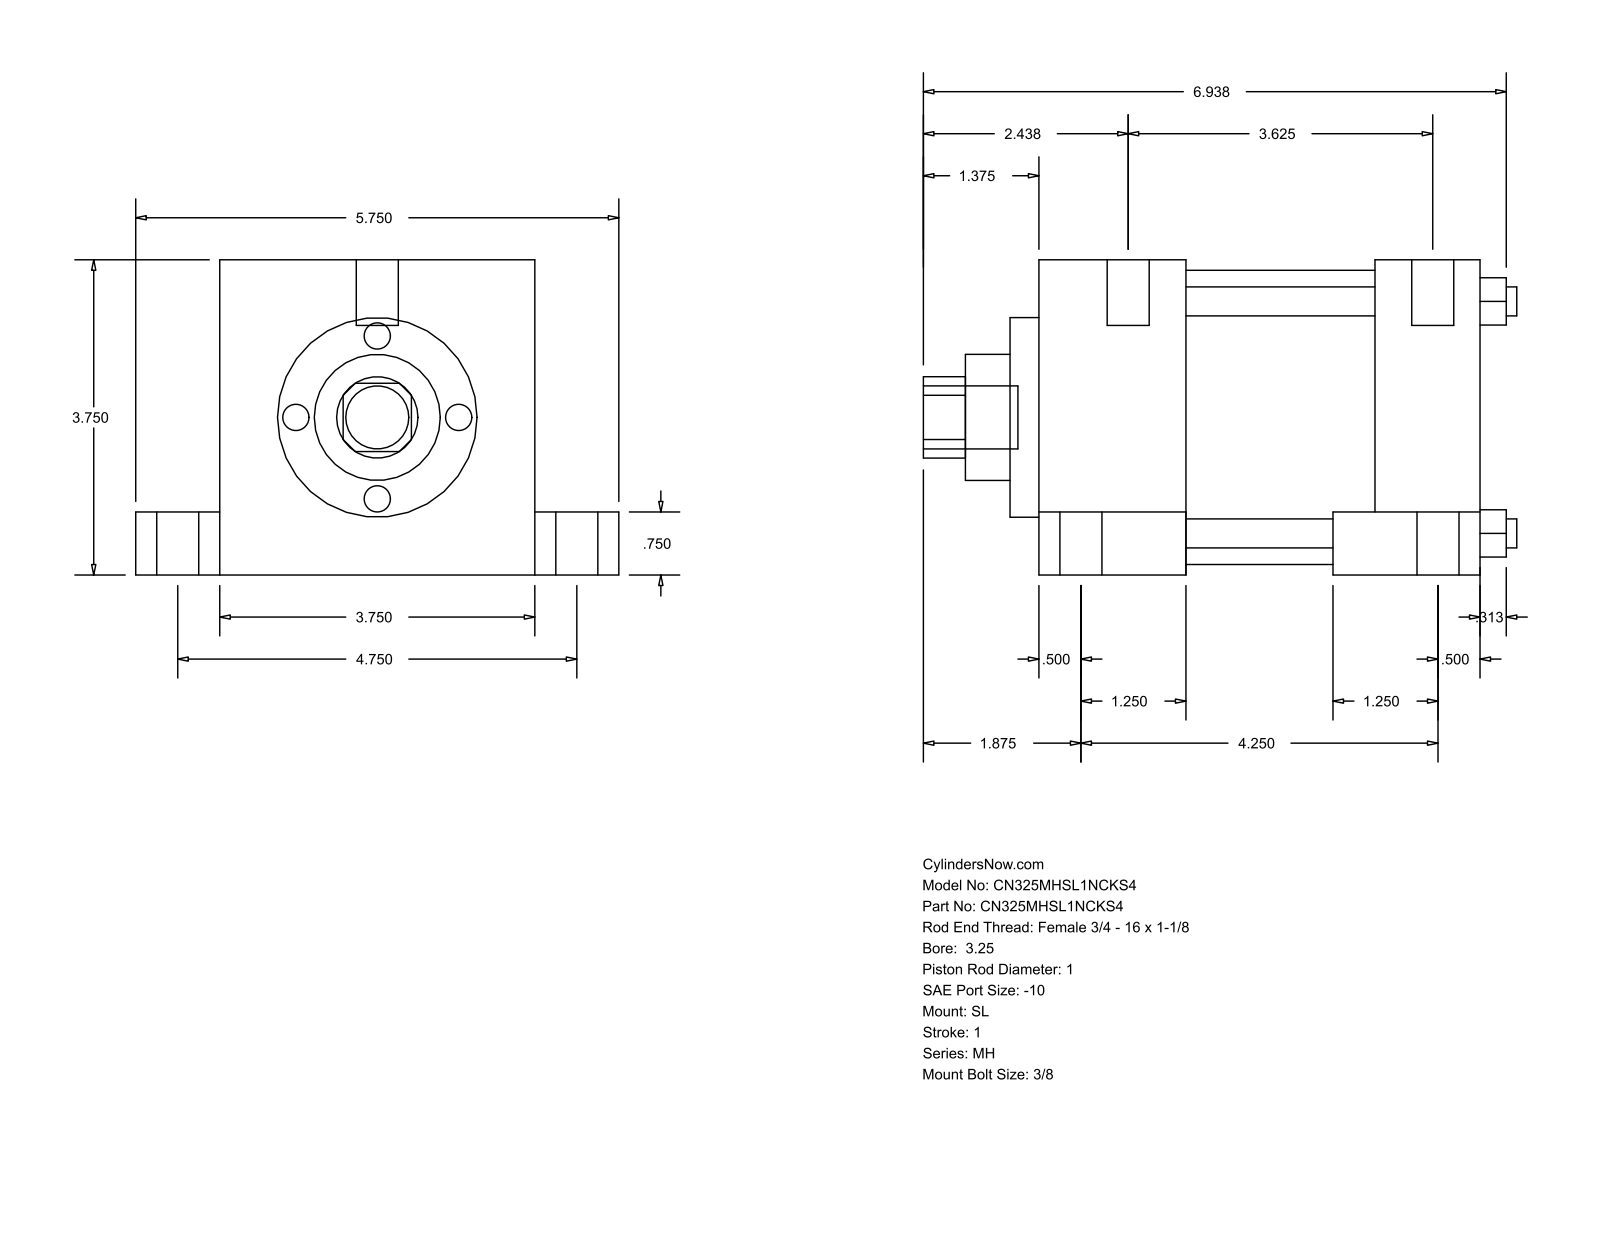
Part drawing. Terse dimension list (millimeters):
name: MH_SL__0325_1
written by: GSSL Pune (CONFIG_CONTROL_DESIGN)
unit: mm
bodies: 0 solids, 110 faces (77 planar, 33 cylindrical, 0 other)
size: 179.39 × 146.05 × 95.25
holes: 4× ⌀8.76, 1× ⌀25.4, 1× ⌀38.1, 1× ⌀60.33, 1× ⌀88.9
bosses: 6× ⌀12.7, 5× ⌀19.05, 4× ⌀5.56
rounds: 1× R12.29
face distances: 95.24, 133.36, 44.46, 88.9, 25.41, 120.65, 19.05, 76.19, 101.61, 57.15
hole spacings: 49.57, 70.1, 99.14
